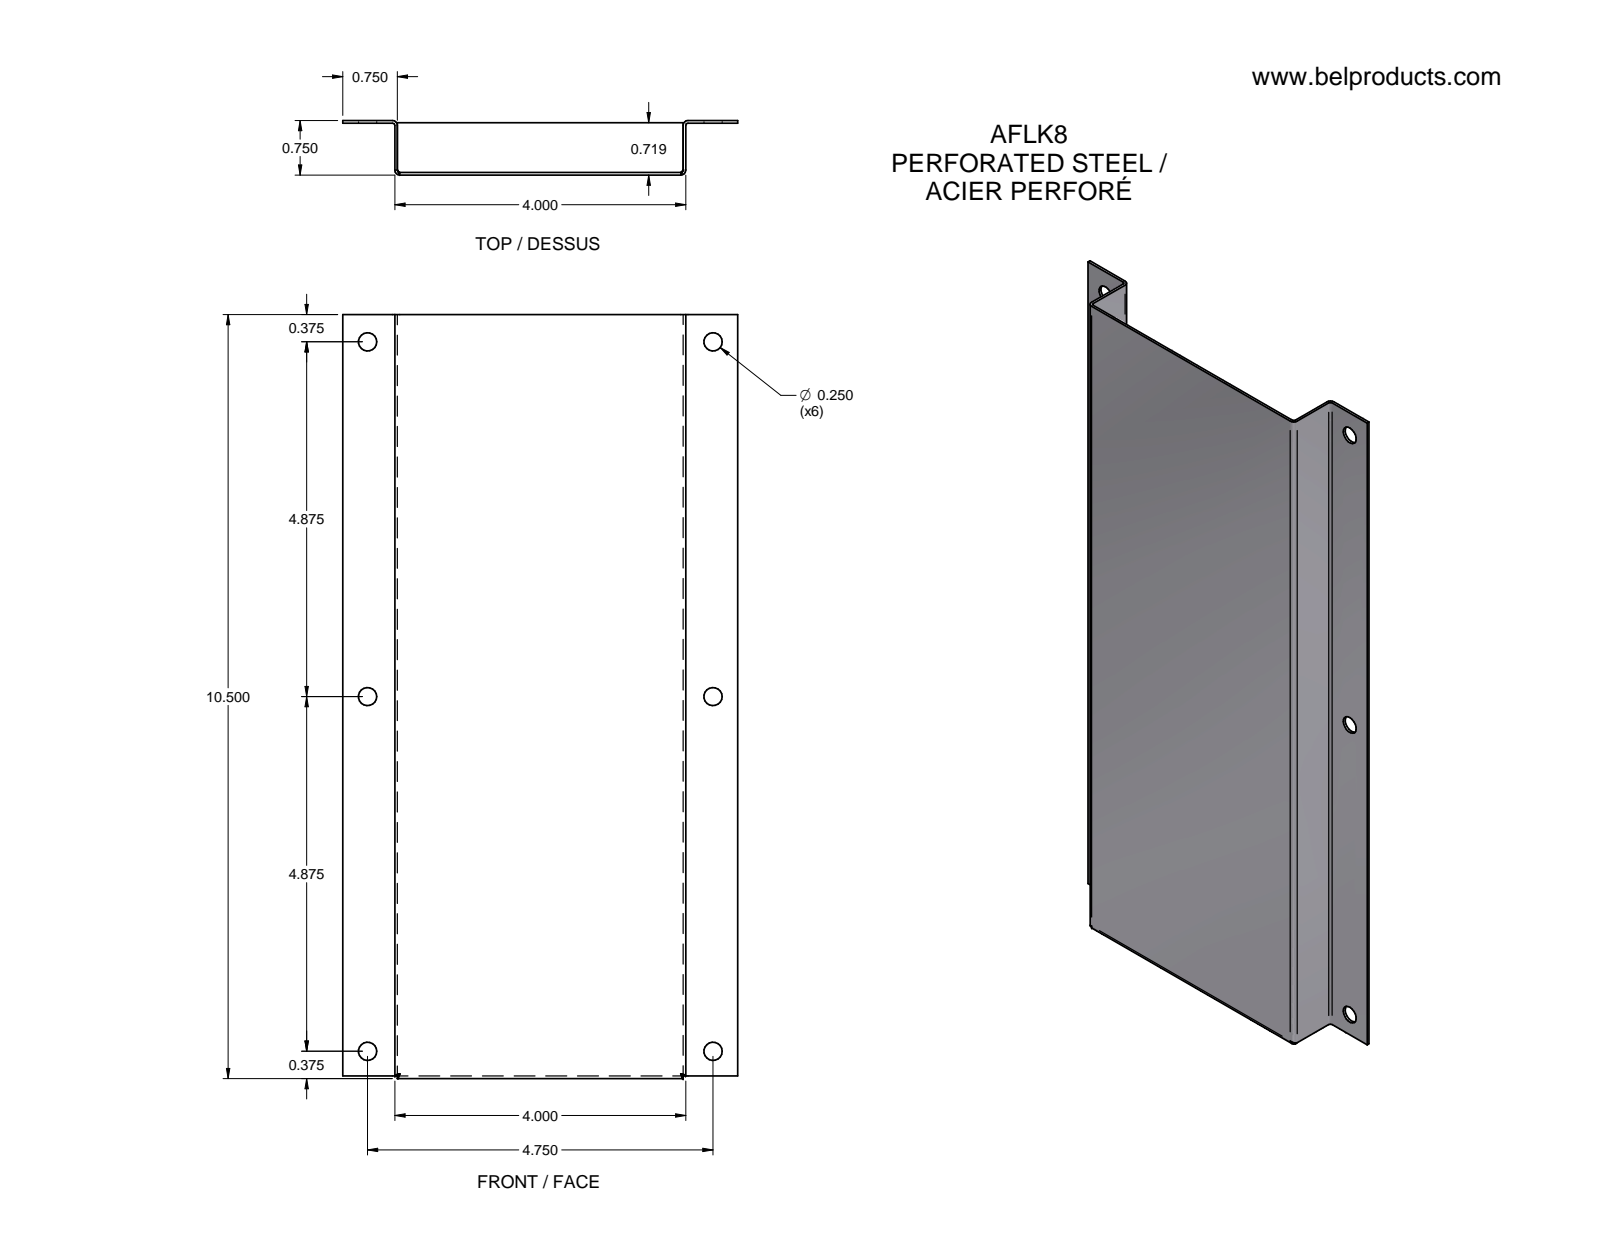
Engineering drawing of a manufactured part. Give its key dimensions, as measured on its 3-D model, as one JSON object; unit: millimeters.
{"step_written_by": "Unknown (AUTOMOTIVE_DESIGN)", "units": "millimeters", "bodies": {"solids": 1, "faces": 40, "planar": 20, "cylindrical": 16, "other": 4}, "overall_size": [266.7, 137.87, 19.05], "volume_mm3": 43233, "surface_area_mm2": 95506, "round_holes": [[6.35, 6]], "partial_cylinders_radius": [[0.81, 5], [1.73, 5]], "face_to_face_distances": [0.91, 18.14, 19.05, 17.23, 100.69, 101.6, 99.78, 118.83, 119.74, 137.88], "hole_center_spacings": [123.83, 172.9, 120.66, 247.66, 275.49]}
